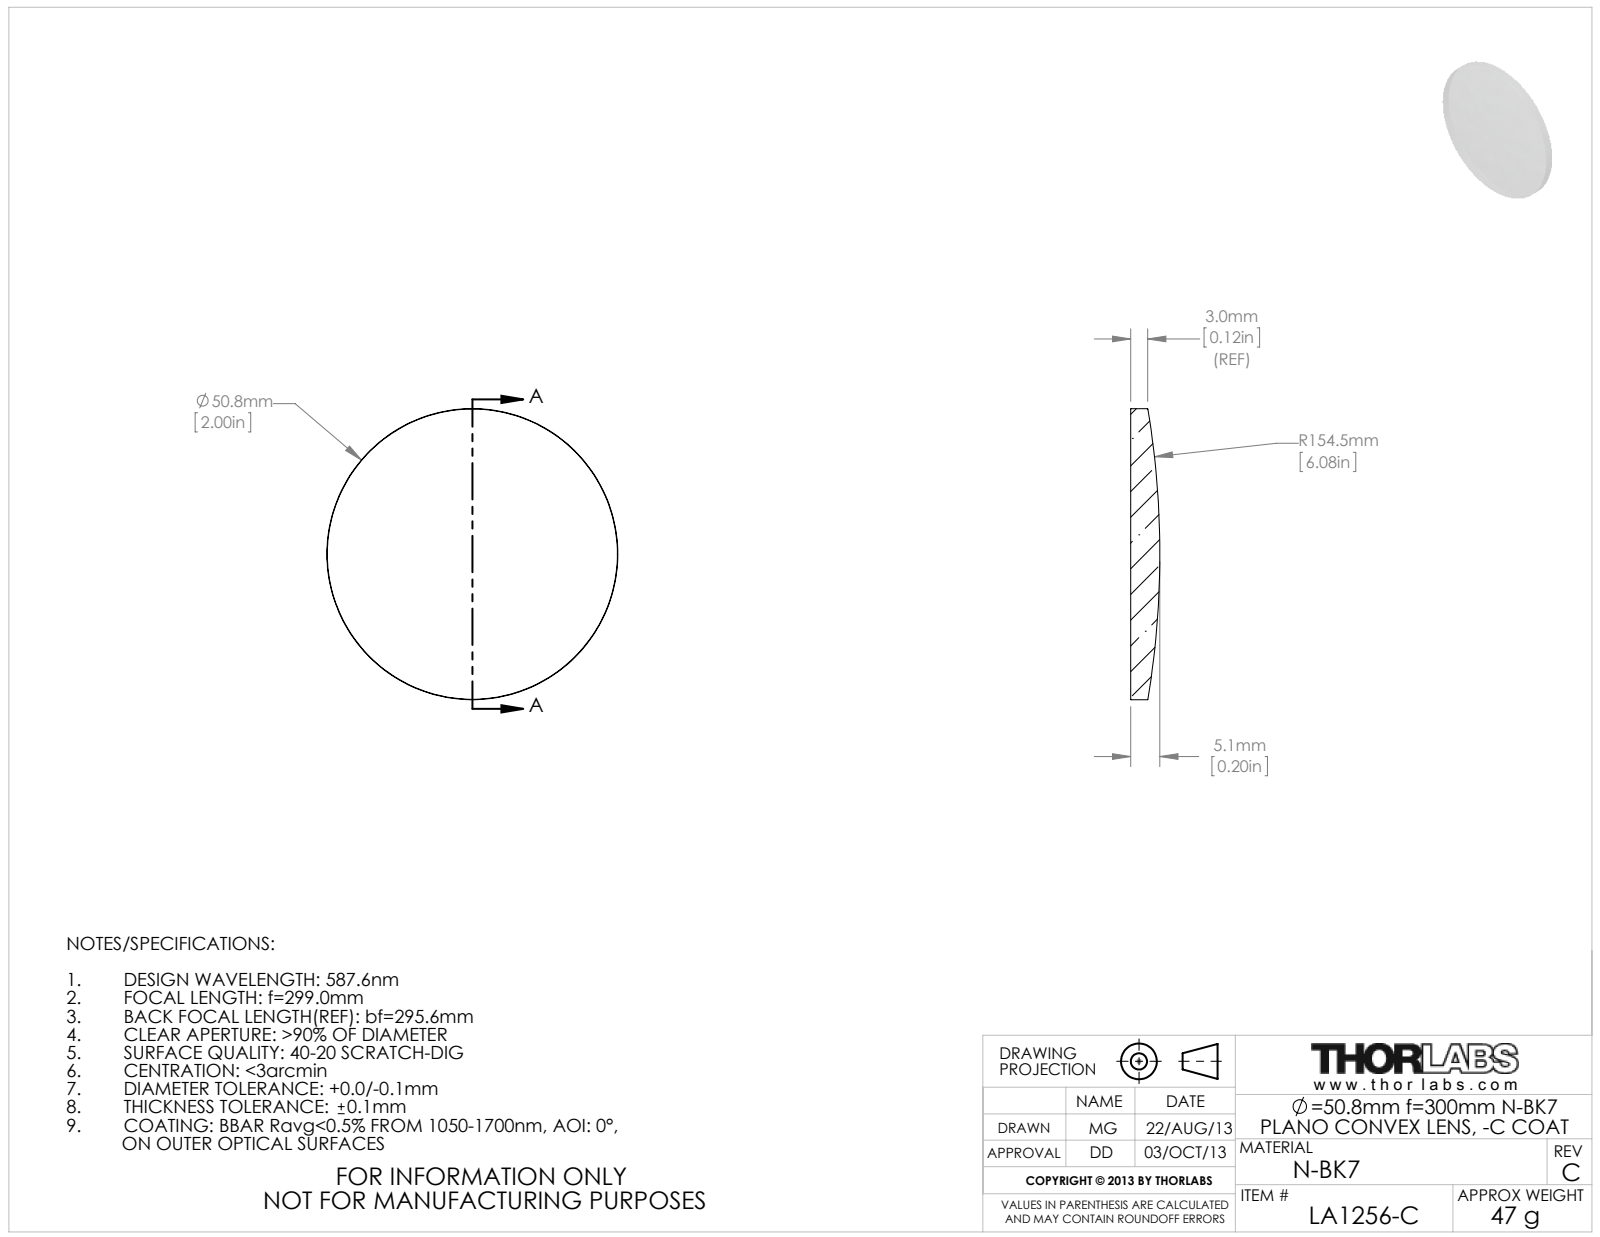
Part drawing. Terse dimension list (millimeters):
name: 4608-E0W
written by: SolidWorks 2009 (AUTOMOTIVE_DESIGN)
unit: mm
bodies: 0 solids, 5 faces (1 planar, 2 cylindrical, 2 other)
size: 50.8 × 50.8 × 5.1
bosses: 1× ⌀50.8
